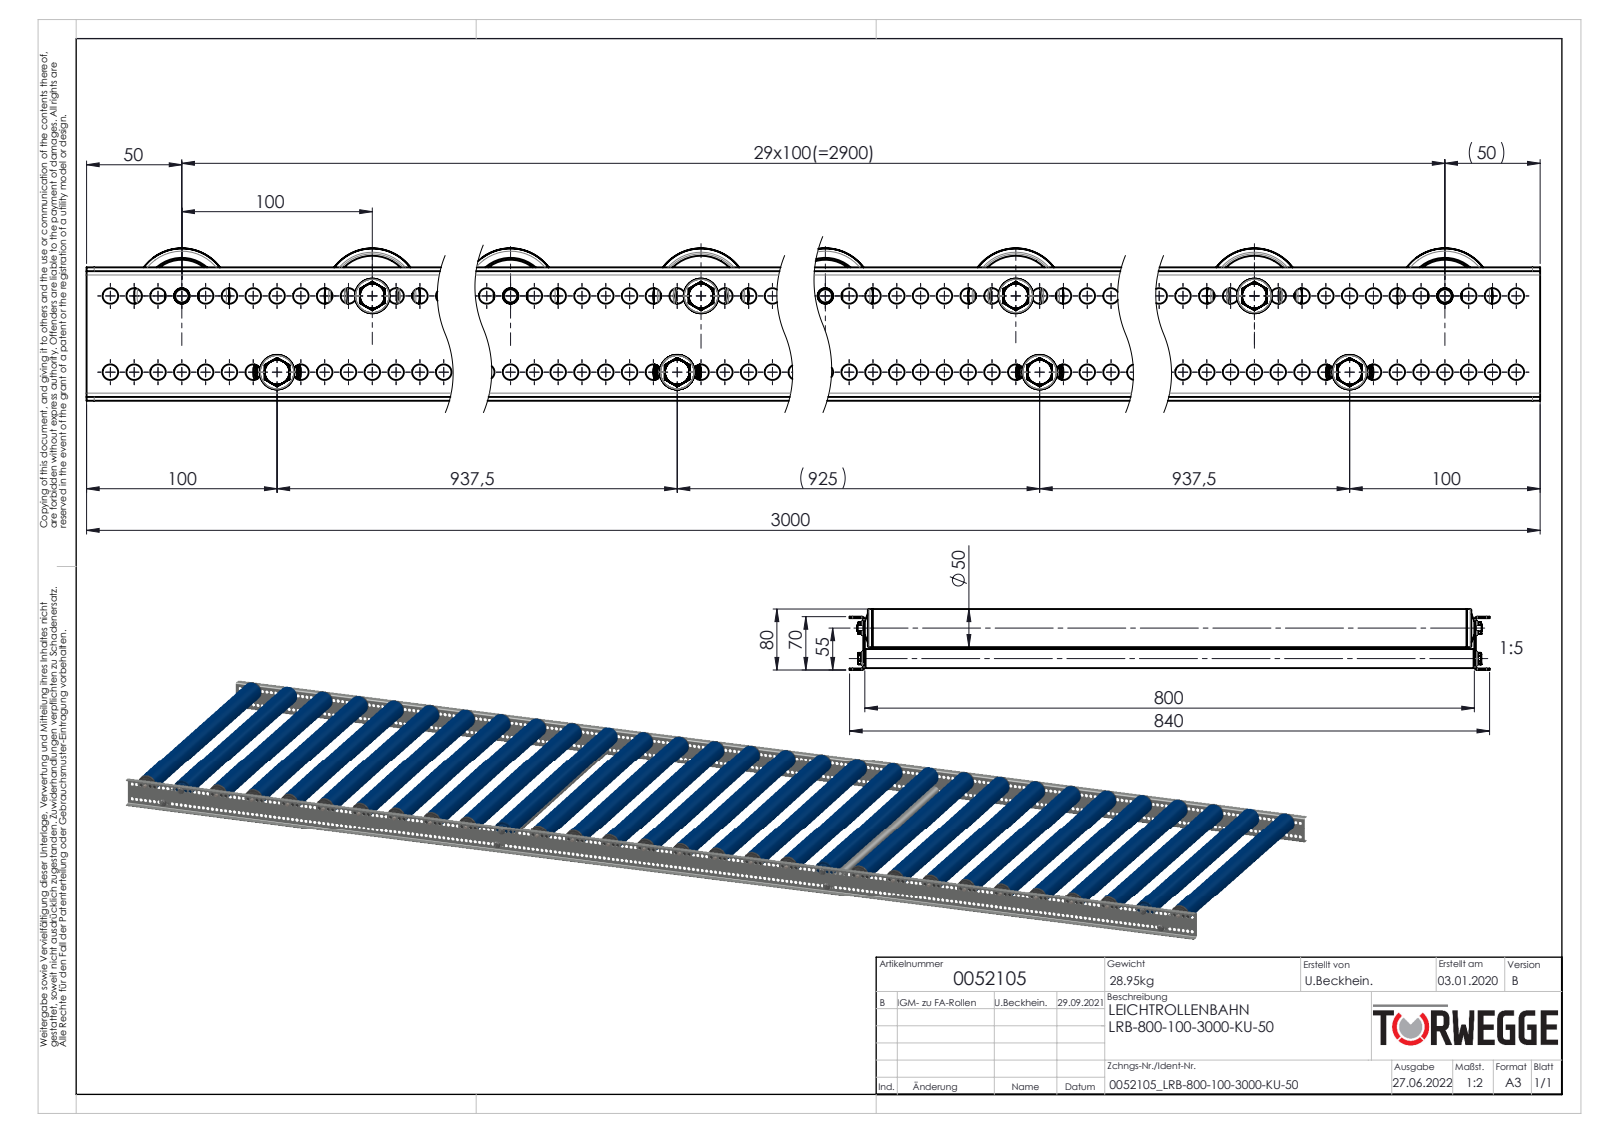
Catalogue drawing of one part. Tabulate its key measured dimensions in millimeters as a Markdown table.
| quantity | value |
| --- | --- |
| part name | KUT100-50x2,8-KB-A8-FA_KFG_0054463_KUT100-50x2,8-KB-A8-FA-EL=800; Traversen_KFG_L800; 0026266_Typ-KUT100-50x2,8-12; 0039778-Achse-ST-Ø08-KFG_AL820-G (+8 more) |
| STEP written by | SolidWorks 2020 (AUTOMOTIVE_DESIGN) |
| units | millimeters |
| bodies | 529 solids, 10474 faces (2574 planar, 4860 cylindrical, 3040 other) |
| overall size | 3000 × 840 × 80 |
| volume | 14 550 000 mm³ |
| surface area | 10 690 000 mm² |
| round holes (diameter × count) | 8.2 × 478, 7.6 × 26, 8 × 26, 25 × 26, 30 × 26, 35 × 26, 39.4 × 26, 40 × 26, 6.8 × 8, 12 × 4, 12.1 × 4, 16 × 4 |
| round bosses / shafts (diameter × count) | 50 × 30, 44.4 × 26, 38 × 26, 36 × 26, 33 × 26, 22 × 26, 21 × 26, 25 × 8 |
| partial cylindrical surfaces (radius × count) | 0.6 × 52, 0.75 × 52, 2.45 × 52, 4.87 × 26, 7 × 26, 2.5 × 16, 4 × 8, 2 × 4 |
| main face-to-face distances | 2, 802, 68, 800, 804, 70, 66, 792, 6, 12 |
| hole center spacings | 12.5, 25, 37.5, 50, 62.5, 75, 87.5, 100 |
